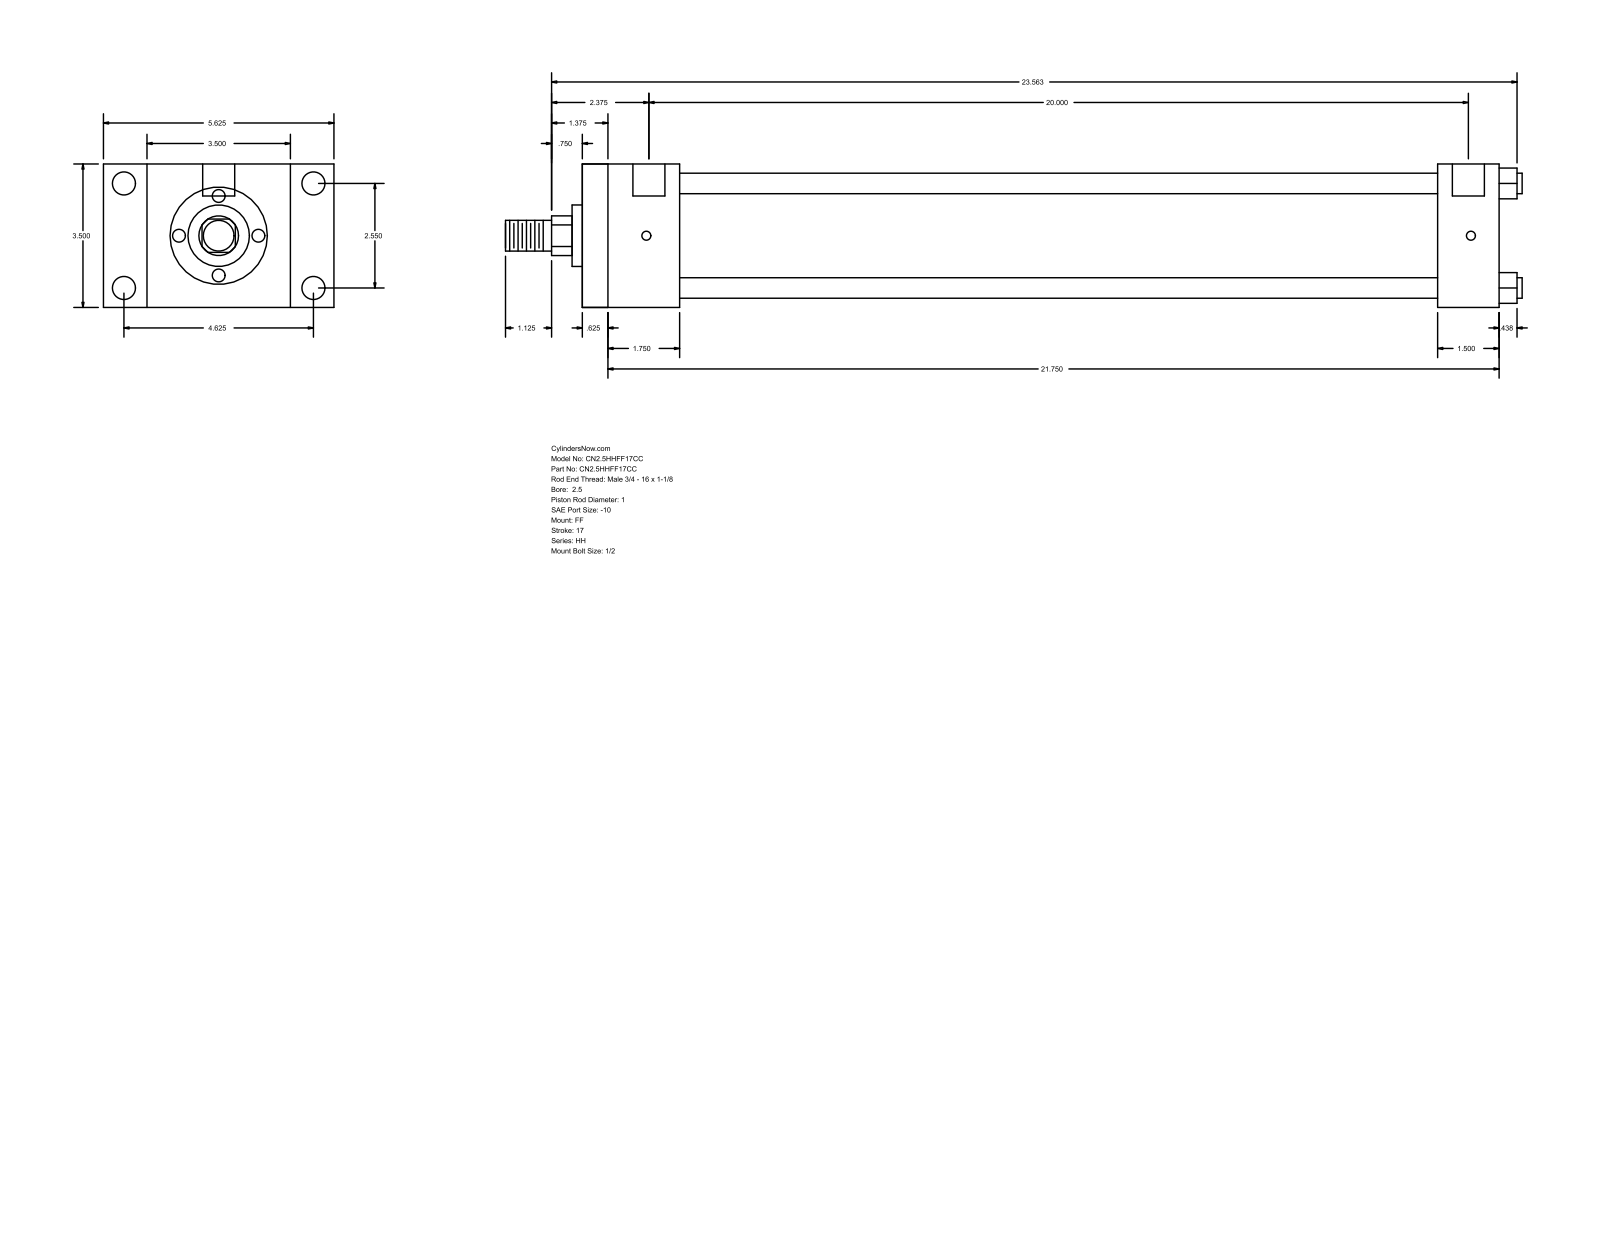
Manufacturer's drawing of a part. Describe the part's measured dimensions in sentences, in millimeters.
The part is named "HH_FF__0250_1". Its 3-D file was written by "GSSL Pune (CONFIG_CONTROL_DESIGN)". It is 0 solids with 92 faces: 64 planar, 28 cylindrical and 0 other. Overall it measures 630.24 by 142.88 by 88.9 millimeters. Round holes: 4 of diameter 5.56, 4 of diameter 14.3, 2 of diameter 19.84. Round bosses or shafts: 4 of diameter 12.7, 1 of diameter 73.03, 1 of diameter 38.1, 1 of diameter 25.4, 1 of diameter 19.05. Partial cylindrical surfaces (rounded edges, fillets, slot ends): 1 of radius 12.29. The main face-to-face distances are 88.9, 568.33, 15.87, 552.46, 60.33, 44.46, 508, 530.22, 514.35, 469.89. The hole center spacings are 64.76, 117.48, 134.15, 511.17, 1.58, 1.59, 508, 509.58.
